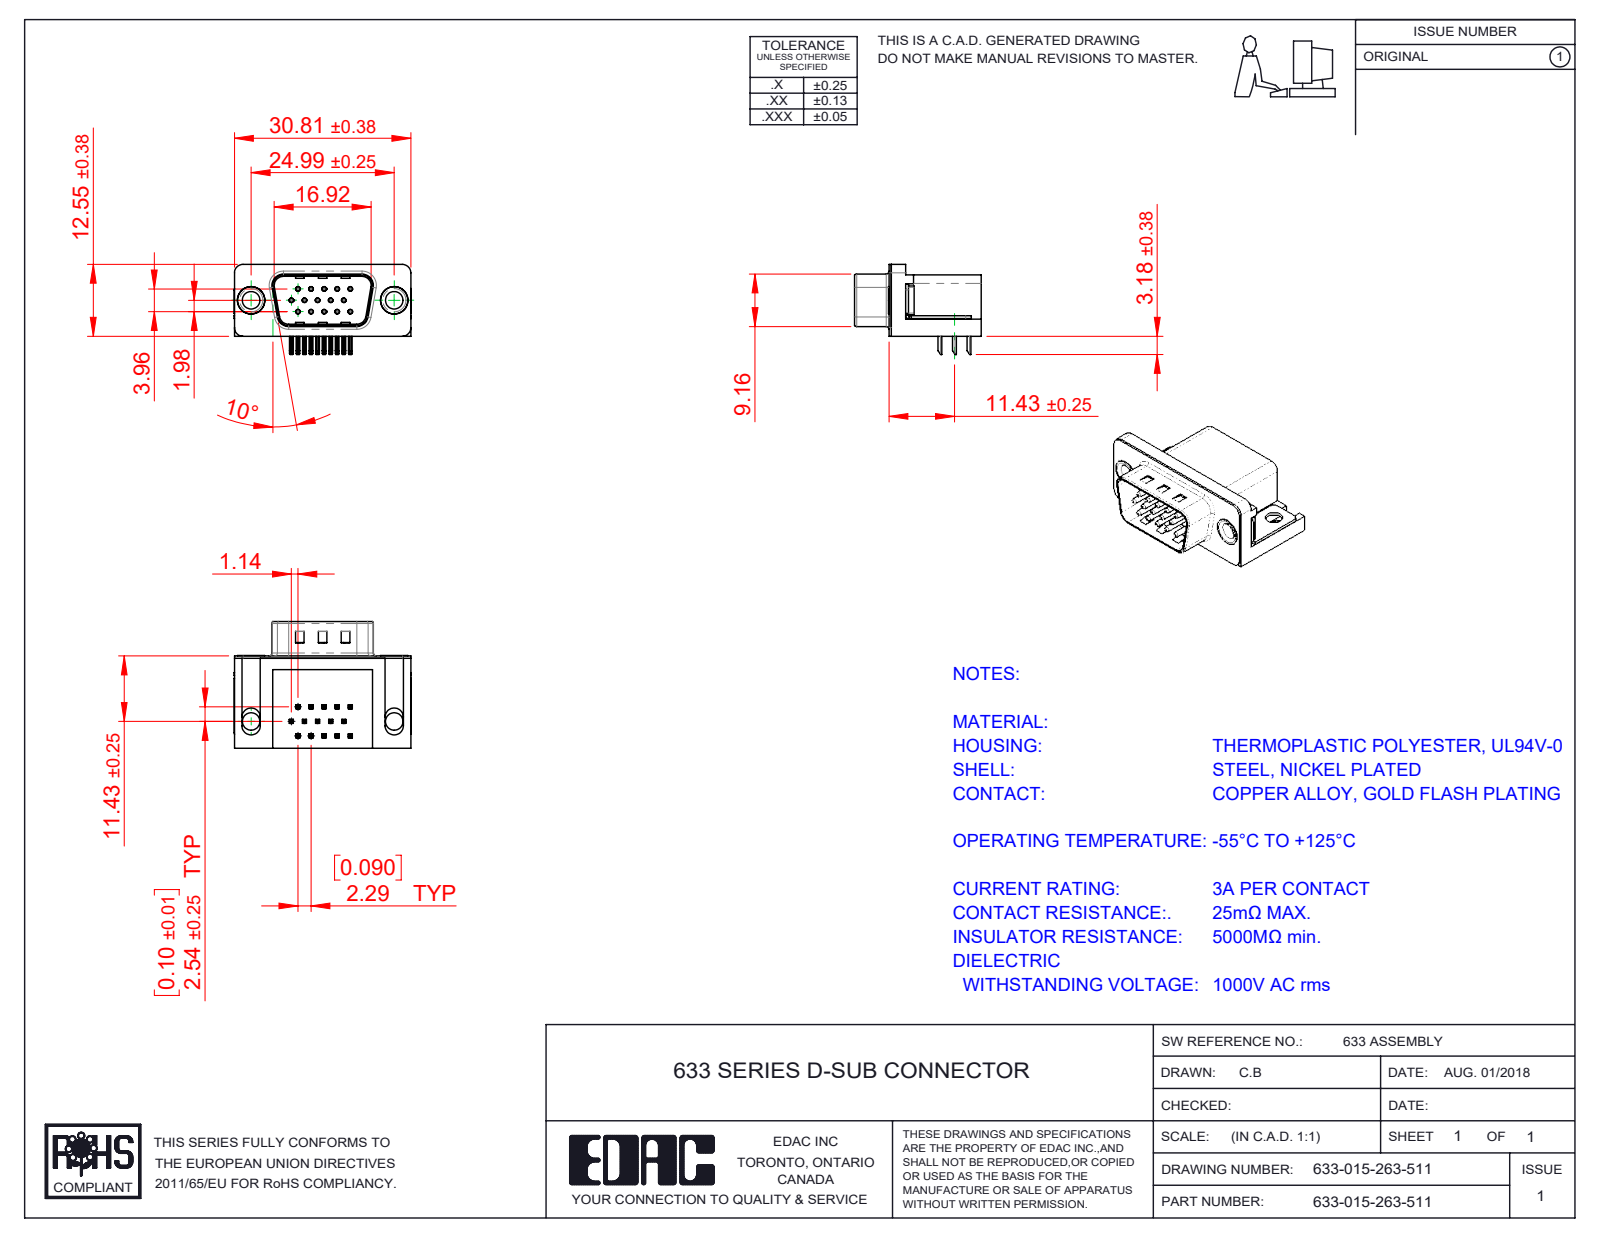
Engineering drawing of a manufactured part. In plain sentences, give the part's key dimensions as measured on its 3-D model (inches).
The part is named "633 Thru Hole Board Mount; 633 Shell_15 Contact; 633 Contact Middle; 633-015-263-511 (+4 more)". Its 3-D file was written by "SolidWorks 2016 (CONFIG_CONTROL_DESIGN)". It is 21 solids with 1401 faces: 859 planar, 425 cylindrical and 117 other. Overall it measures 1.216 by 0.87 by 0.619 inches. Its volume is 0.248 cubic inches and its surface area 8.361 square inches. Round holes: 15 of diameter 0.014, 15 of diameter 0.031, 4 of diameter 0.12, 2 of diameter 0.157, 2 of diameter 0.189, 2 of diameter 0.197. Round bosses or shafts: 15 of diameter 0.03, 2 of diameter 0.193, 2 of diameter 0.187, 2 of diameter 0.152. Partial cylindrical surfaces (rounded edges, fillets, slot ends): 68 of radius 0.01, 30 of radius 0.005, 16 of radius 0.039, 9 of radius 0.02, 8 of radius 0.063, 7 of radius 0.059, 4 of radius 0.035, 4 of radius 0.079. The main face-to-face distances are 0.016, 0.407, 0.618, 0.02, 0.114, 0.098, 0.264, 0.634, 0.014, 0.421. The hole center spacings are 0.156, 0.09, 0.18, 0.09, 0.238, 0.27, 0.312, 0.238.
